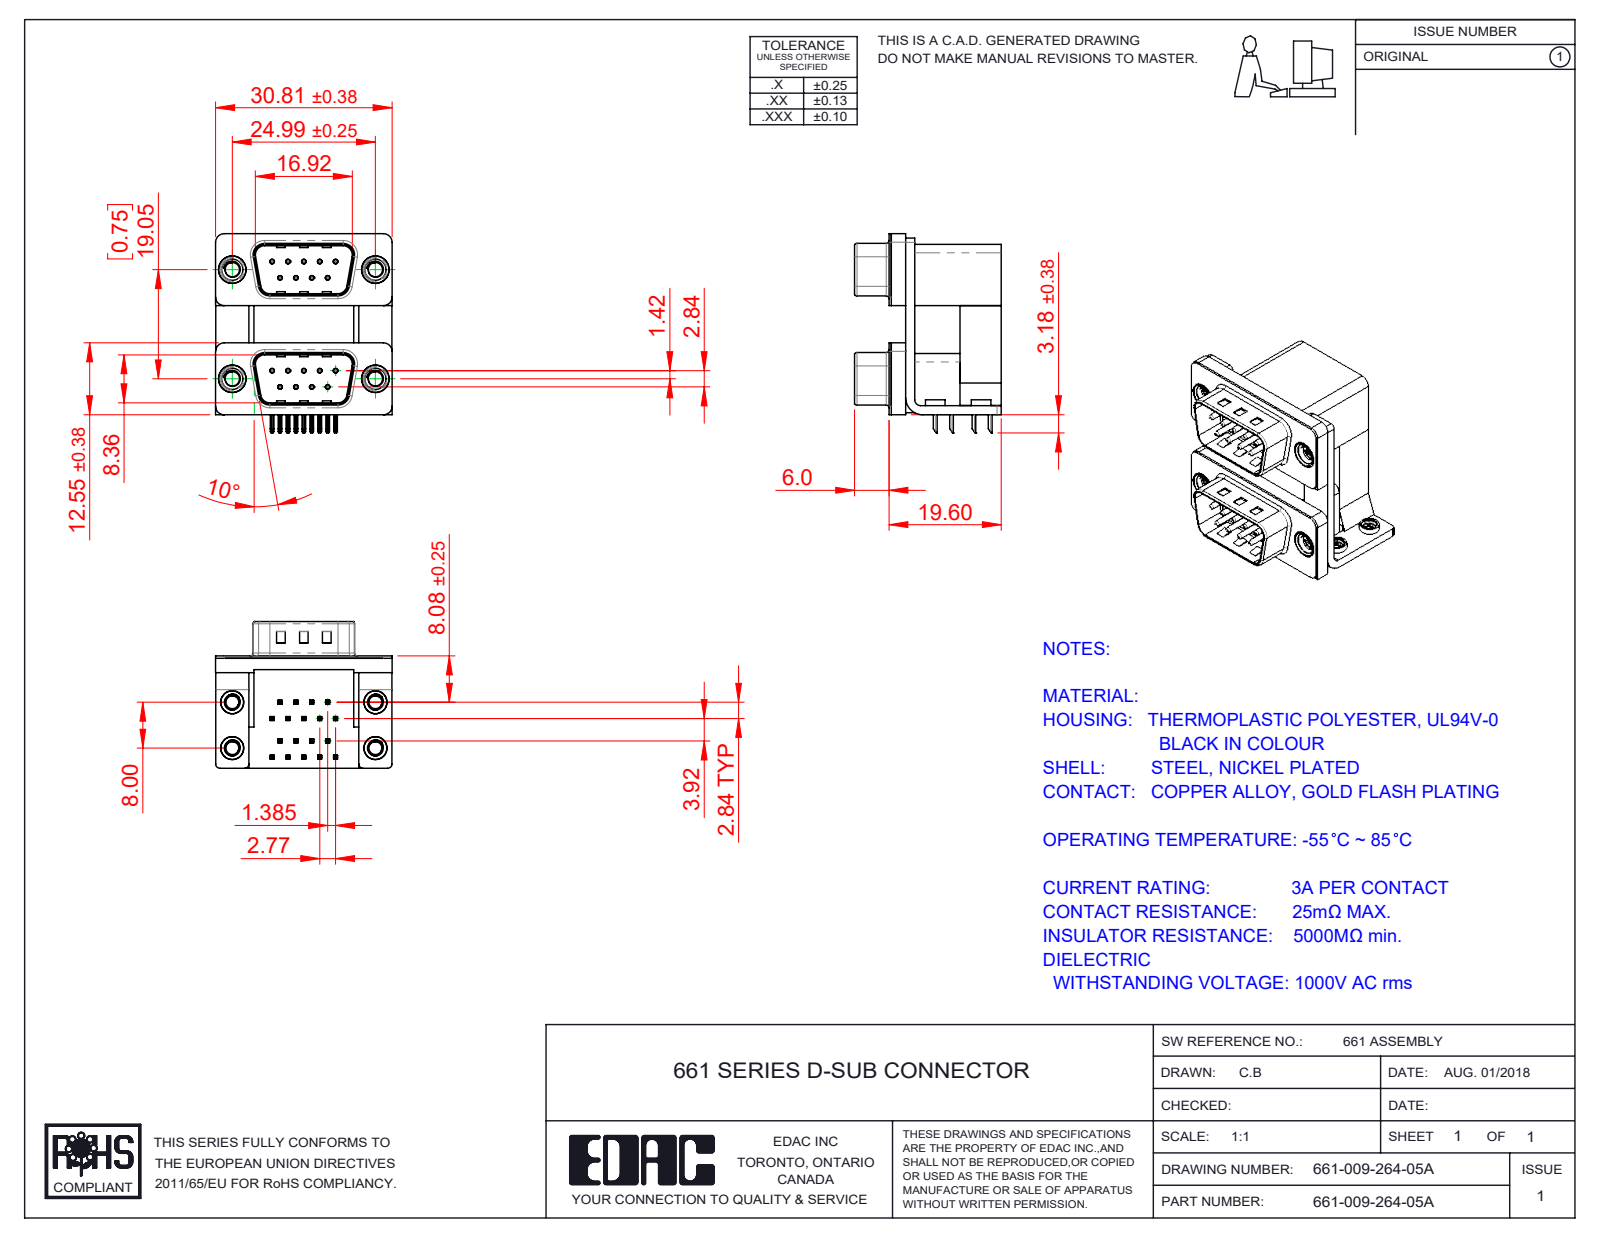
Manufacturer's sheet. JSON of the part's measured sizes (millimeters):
{"part_name": "661 Shell_09 Contacts; 661 Mounting Bracket_ThruM; 661 Housing Upper_09 Contacts M; 661 Contact Bottom Upper_M (+8 more)", "step_written_by": "SolidWorks 2020 (CONFIG_CONTROL_DESIGN)", "units": "millimeters", "bodies": {"solids": 33, "faces": 2092, "planar": 1164, "cylindrical": 678, "other": 250}, "overall_size": [34.78, 30.81, 25.6], "volume_mm3": 10311, "surface_area_mm2": 12085, "round_holes": [[0.35, 18], [0.8, 18], [2.26, 4], [2.5, 4], [2.75, 4], [3.2, 4], [3.5, 4], [4, 4], [4.8, 4], [5, 4]], "round_bosses_or_shafts": [[0.75, 18], [4.9, 4], [4.75, 4], [4, 4], [3.9, 4], [3.4, 4]], "partial_cylinders_radius": [[0.25, 72], [0.12, 36], [0.5, 16], [1.5, 14], [0.75, 8], [0.9, 8], [1.6, 8], [2, 8]], "face_to_face_distances": [0.4, 2.5, 19.05, 16.7, 19.2, 10.69, 7.2, 9.5, 12, 1.6], "hole_center_spacings": [3.16, 2.77, 19.25, 19.05, 5.54, 19.84, 16.27, 21.93]}
